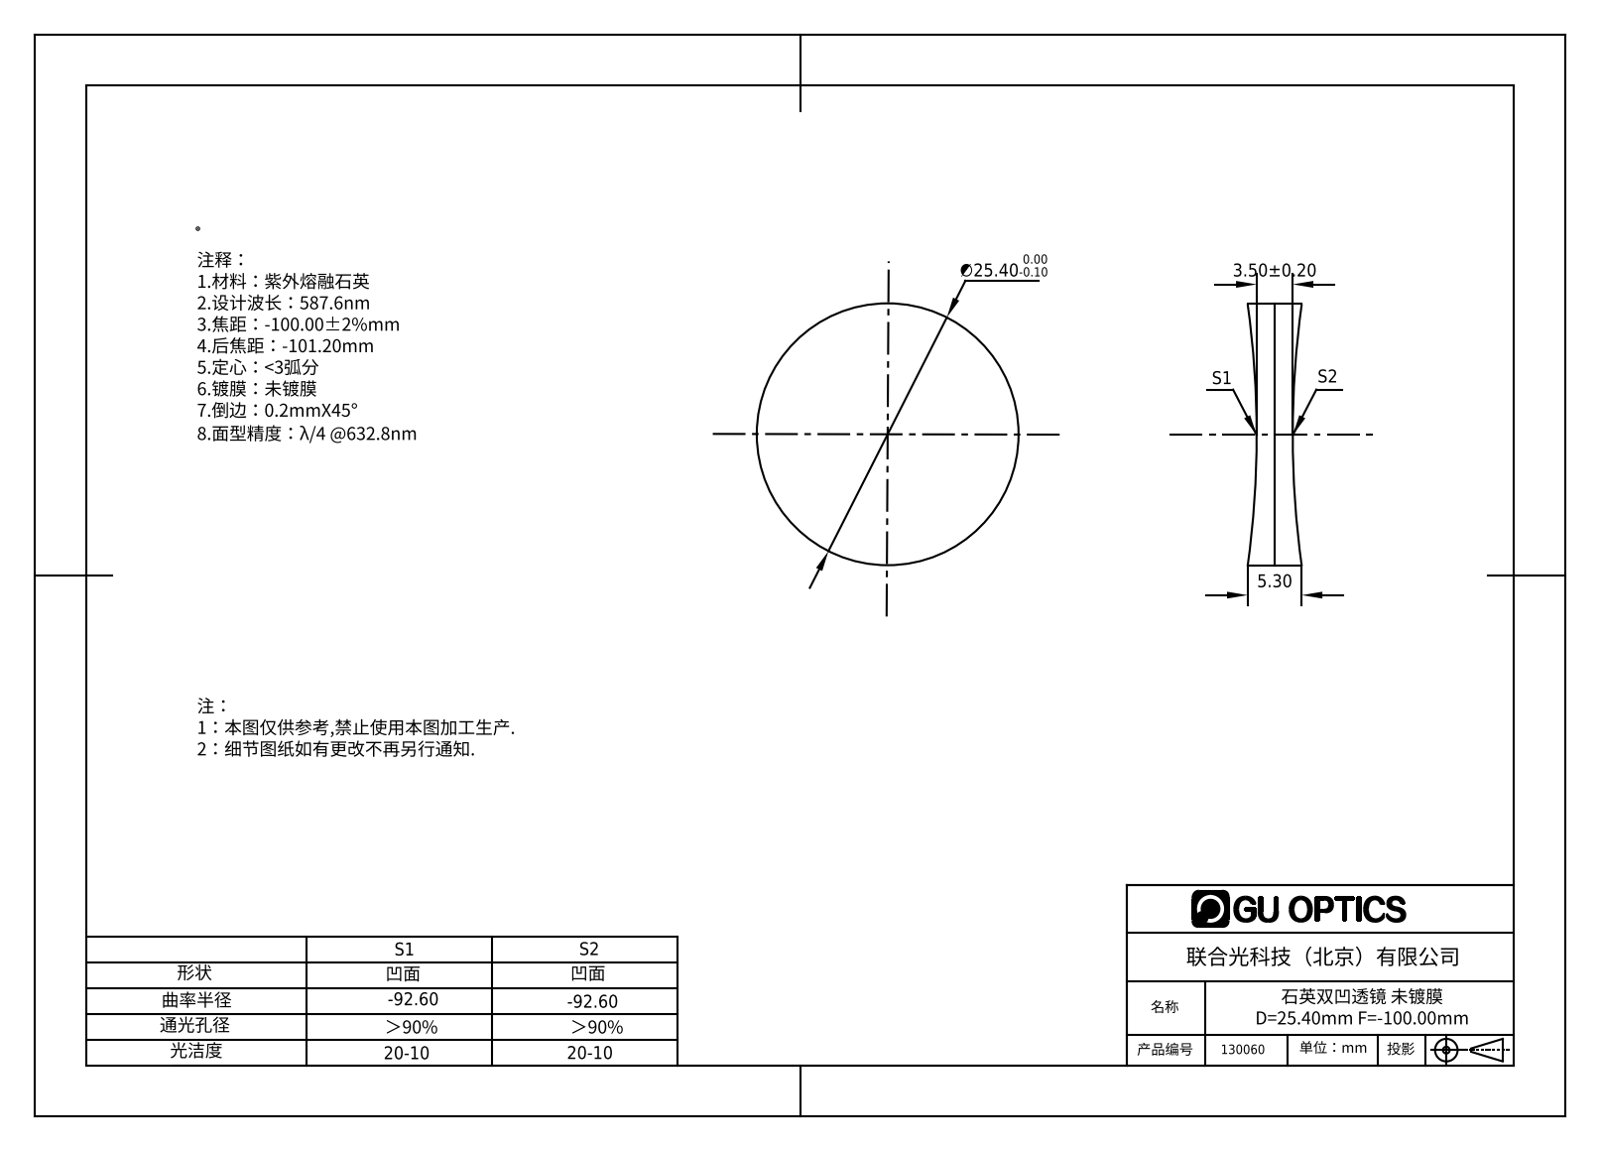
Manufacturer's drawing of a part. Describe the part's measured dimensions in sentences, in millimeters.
The part is named "130060". Its 3-D file was written by "SolidWorks 2016 (AUTOMOTIVE_DESIGN)". It is 1 solid with 6 faces: 0 planar, 2 cylindrical and 4 other. Overall it measures 25.4 by 25.4 by 5.25 millimeters. Its volume is 2 216 cubic millimeters and its surface area 1 437 square millimeters. Round bosses or shafts: 1 of diameter 25.4.
